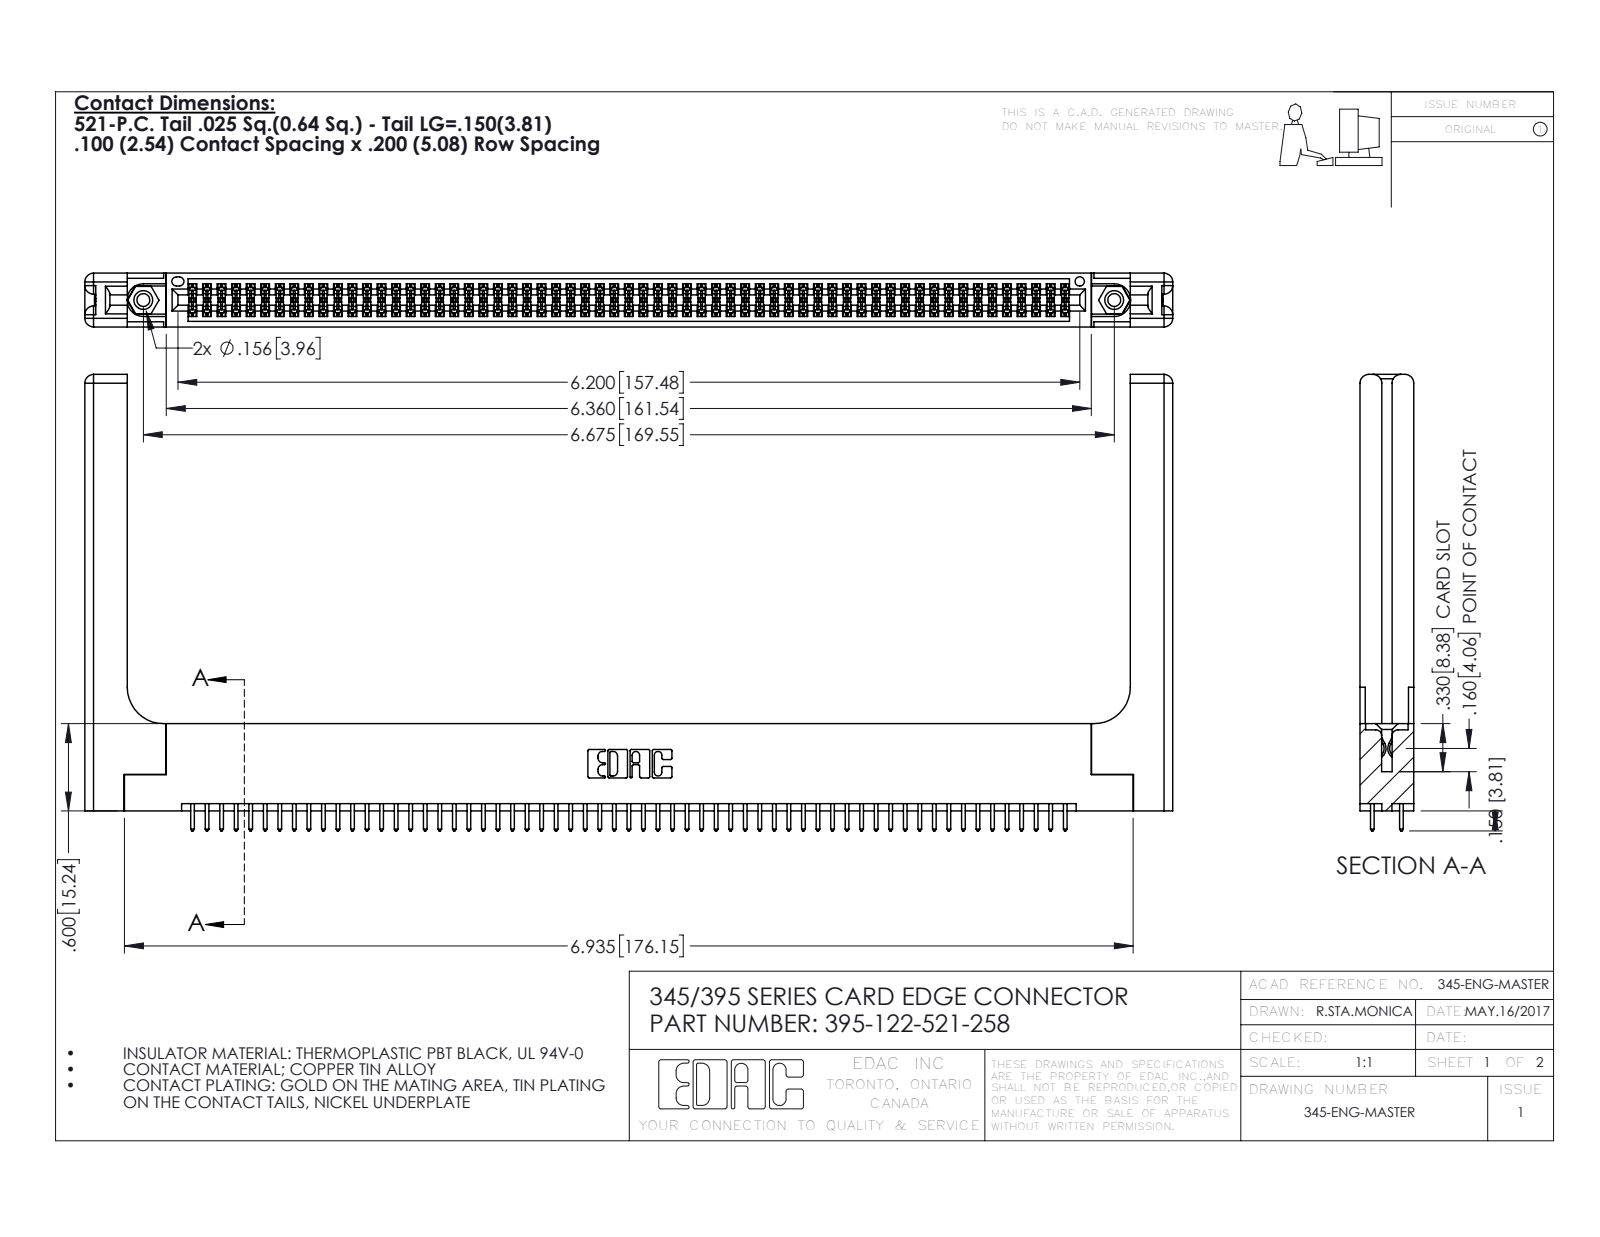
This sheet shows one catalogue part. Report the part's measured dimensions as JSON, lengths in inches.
{"part_name": "345-220-058_345-220-058; 395-122-521-258; 345-292-001_345-293-121; 345 Part_Flush Mounting Lugs - 0.156 Dia-TH (+1 more)", "step_written_by": "SolidWorks 2016 (CONFIG_CONTROL_DESIGN)", "units": "inches", "bodies": {"solids": 127, "faces": 6482, "planar": 4254, "cylindrical": 2168, "other": 60}, "overall_size": [7.479, 3.137, 0.37], "volume_in3": 1.651, "surface_area_in2": 50.48, "round_holes": [[0.089, 2], [0.125, 2], [0.156, 2], [0.064, 1]], "round_bosses_or_shafts": [[0.155, 2]], "partial_cylinders_radius": [[0.006, 183], [0.01, 122], [0.01, 22], [0.06, 16], [0.007, 6], [0.031, 6], [0.026, 3], [0.014, 2]], "face_to_face_distances": [0.072, 0.298, 0.37, 0.2, 0.098, 0.272, 0.025, 0.225, 0.175, 0.148], "hole_center_spacings": [0.27, 6.439, 6.675]}
